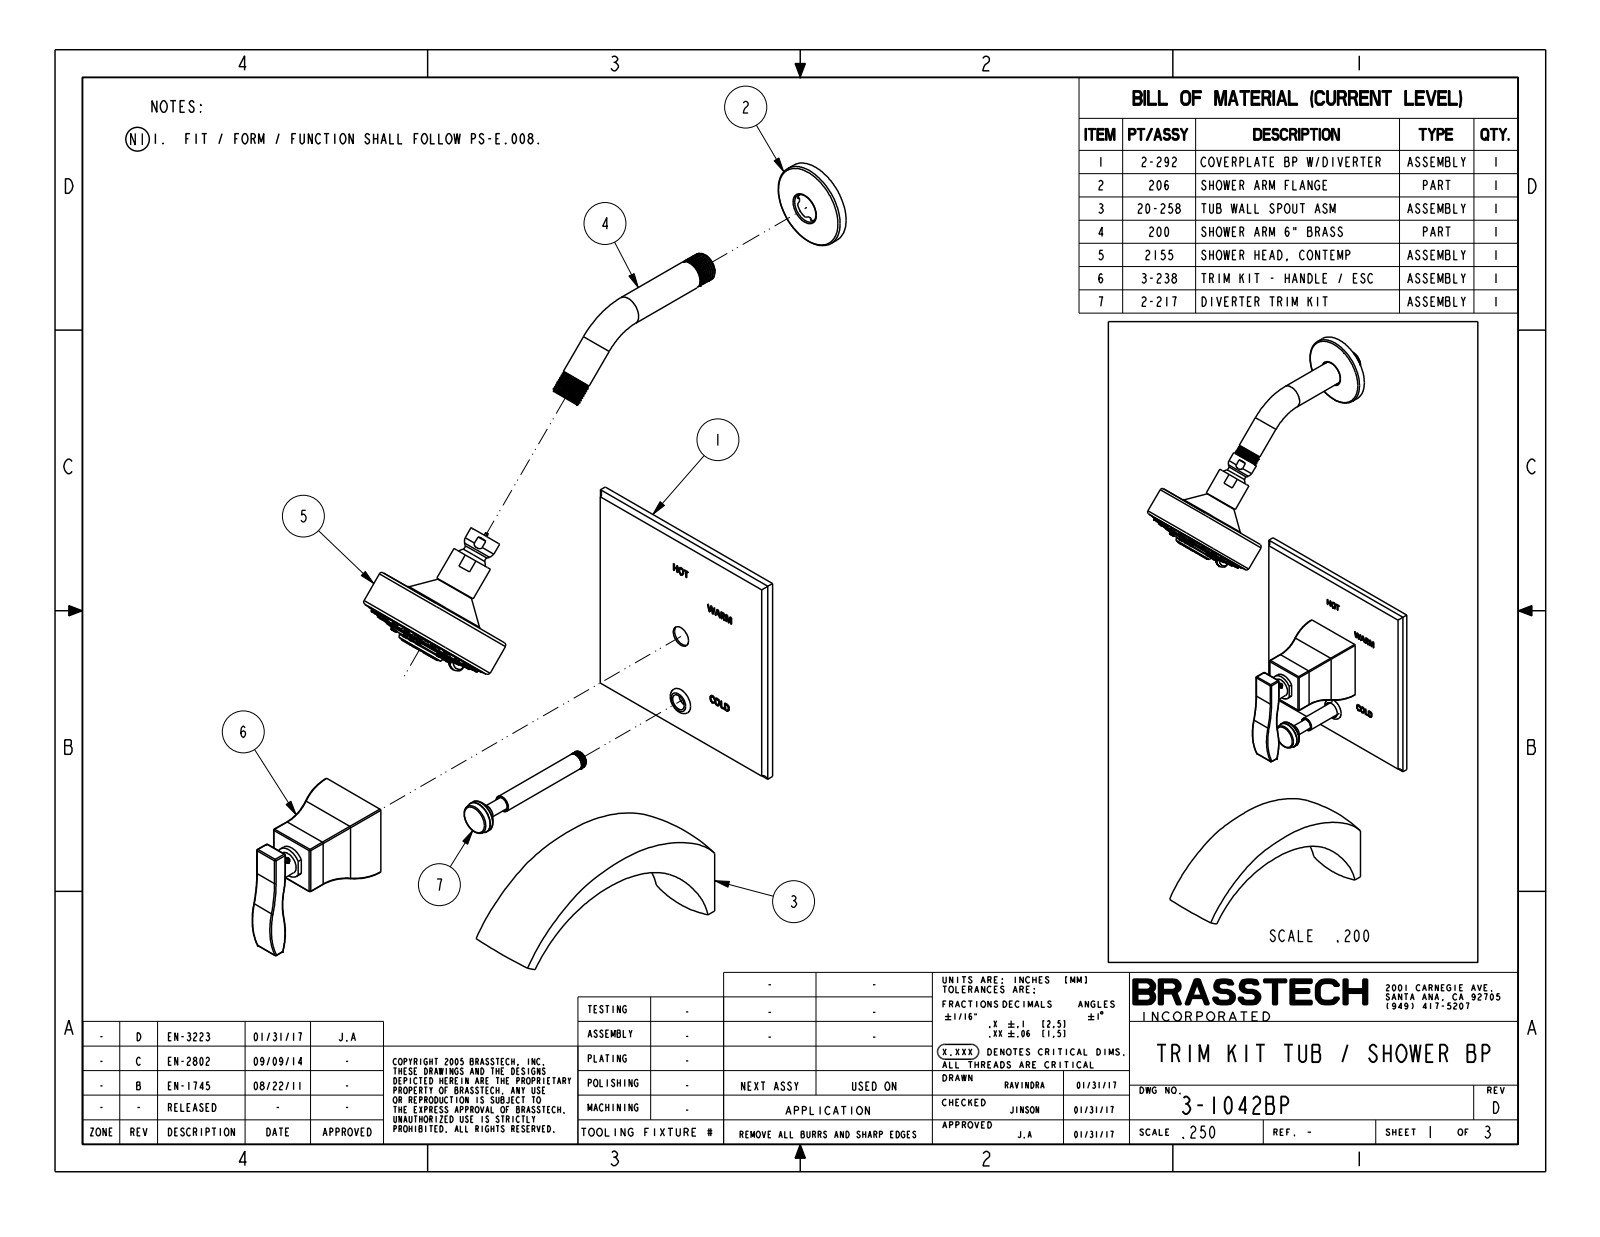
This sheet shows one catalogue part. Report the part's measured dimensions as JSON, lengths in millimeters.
{"part_name": "11000; 91033; H-78; 2-292_ASM (+8 more)", "step_written_by": "PRO/ENGINEER BY PARAMETRIC TECHNOLOGY CORPORATION, 2013150 (CONFIG_CONTROL_DESIGN)", "units": "millimeters", "bodies": {"solids": 51, "faces": 7717, "planar": 3396, "cylindrical": 1806, "other": 2515}, "overall_size": [563.6, 247.2, 165.1], "volume_mm3": 376900, "surface_area_mm2": 515300, "round_holes": [[1.1, 32], [2.5, 15], [1.5, 12], [2, 8], [2.4, 8], [4.7, 8], [3, 7], [3.8, 3], [6.4, 3], [7, 3], [3.3, 2], [6.8, 2]], "round_bosses_or_shafts": [[3.6, 39], [4.2, 23], [8, 3], [6.2, 3], [59, 2], [20.7, 2], [19.5, 2], [16, 2]], "partial_cylinders_radius": [[0.5, 52], [0.8, 30], [0.3, 29], [2.1, 15], [0.2, 14], [1, 12], [1.6, 12], [2, 9]], "face_to_face_distances": [1.3, 2.5, 50.8, 5.3, 7.3, 17.7, 7.8, 1, 16.7, 11.4], "hole_center_spacings": [9.6, 7, 10.7, 12.9, 5.3, 6.1, 7.5, 12.4]}
